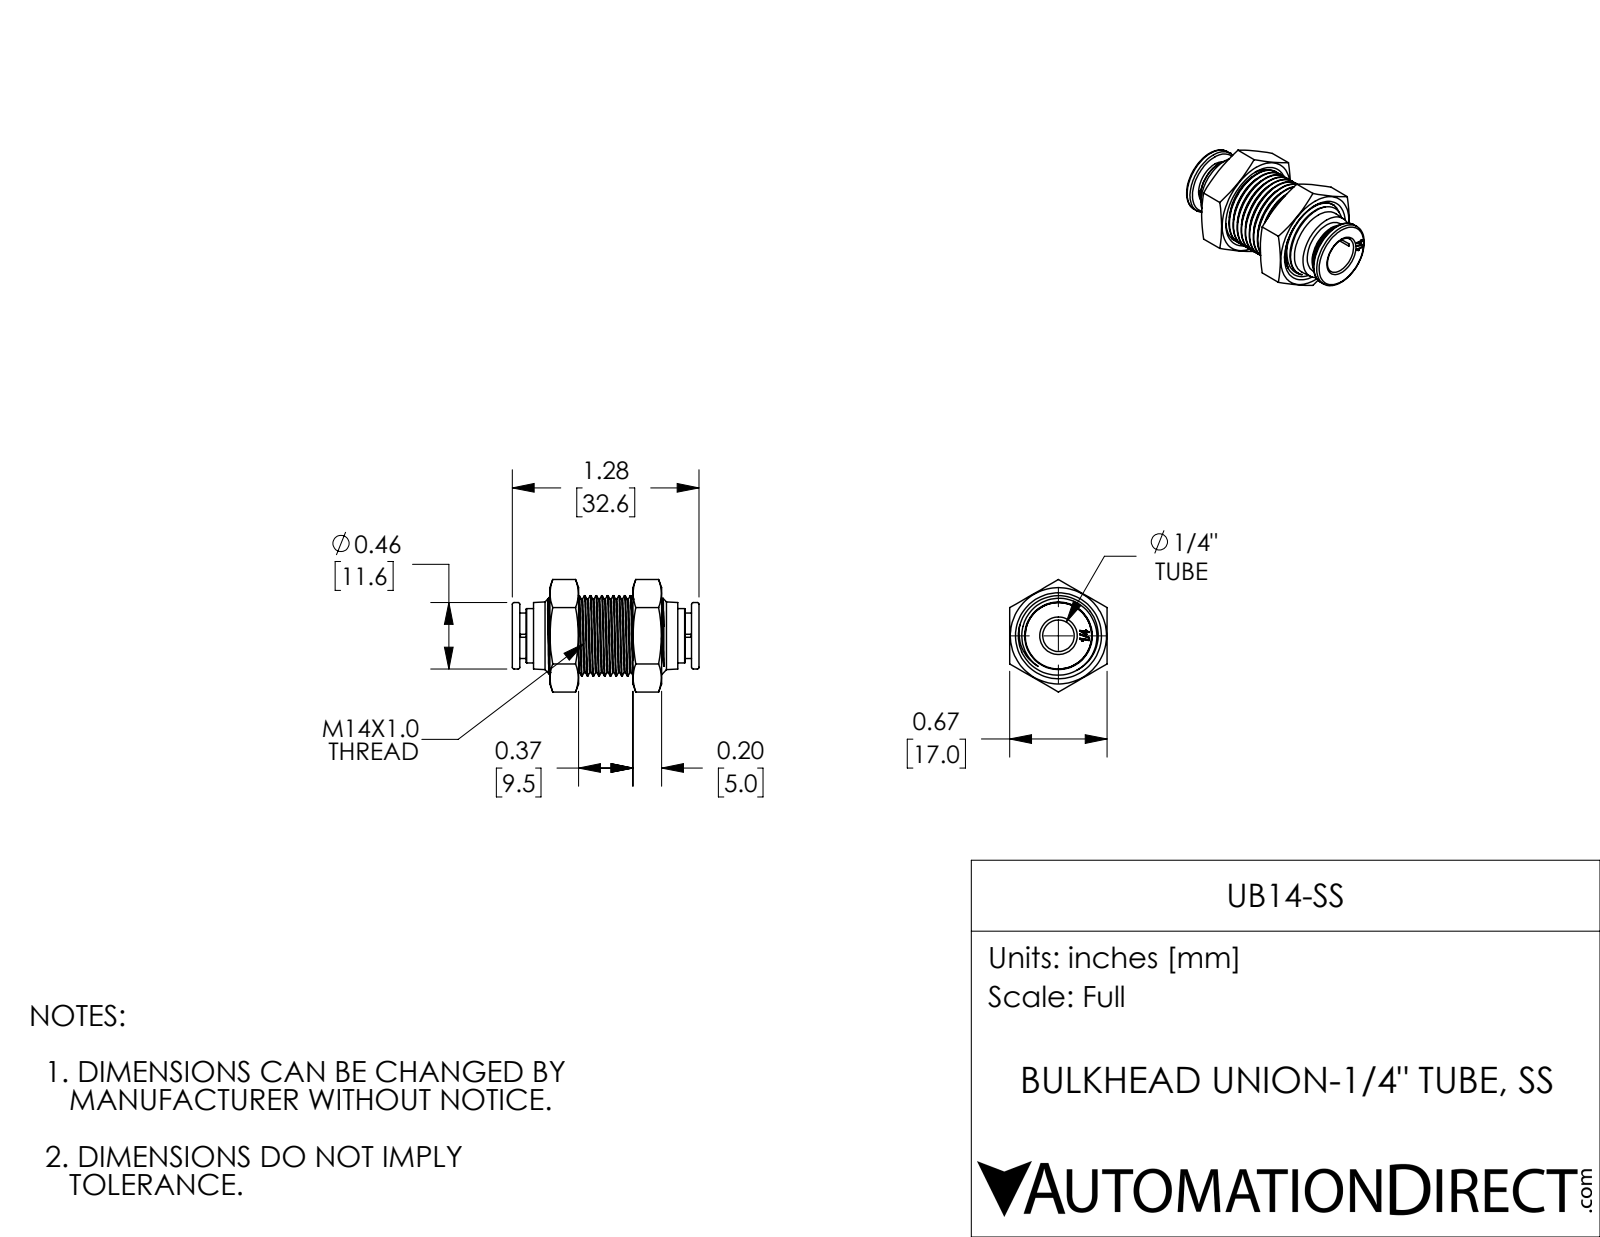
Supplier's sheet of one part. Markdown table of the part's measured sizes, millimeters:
| quantity | value |
| --- | --- |
| part name | UB14-SS |
| STEP written by | SolidWorks 2017 (AUTOMOTIVE_DESIGN) |
| units | millimeters |
| bodies | 1 solid, 256 faces (94 planar, 107 cylindrical, 55 other) |
| overall size | 32.6 × 19.6 × 17 |
| volume | 3 850 mm³ |
| surface area | 3 761 mm² |
| round holes (diameter × count) | 5.5 × 1, 6.6 × 1, 8.1 × 1, 13 × 1 |
| round bosses / shafts (diameter × count) | 14 × 1, 12.8 × 1, 11.6 × 1, 9.5 × 1, 8 × 1 |
| partial cylindrical surfaces (radius × count) | 0.7 × 2 |
| main face-to-face distances | 17, 5.3, 10.3, 14.5, 1.3, 2.4, 28.9, 31.3, 6.6, 11.6 |
